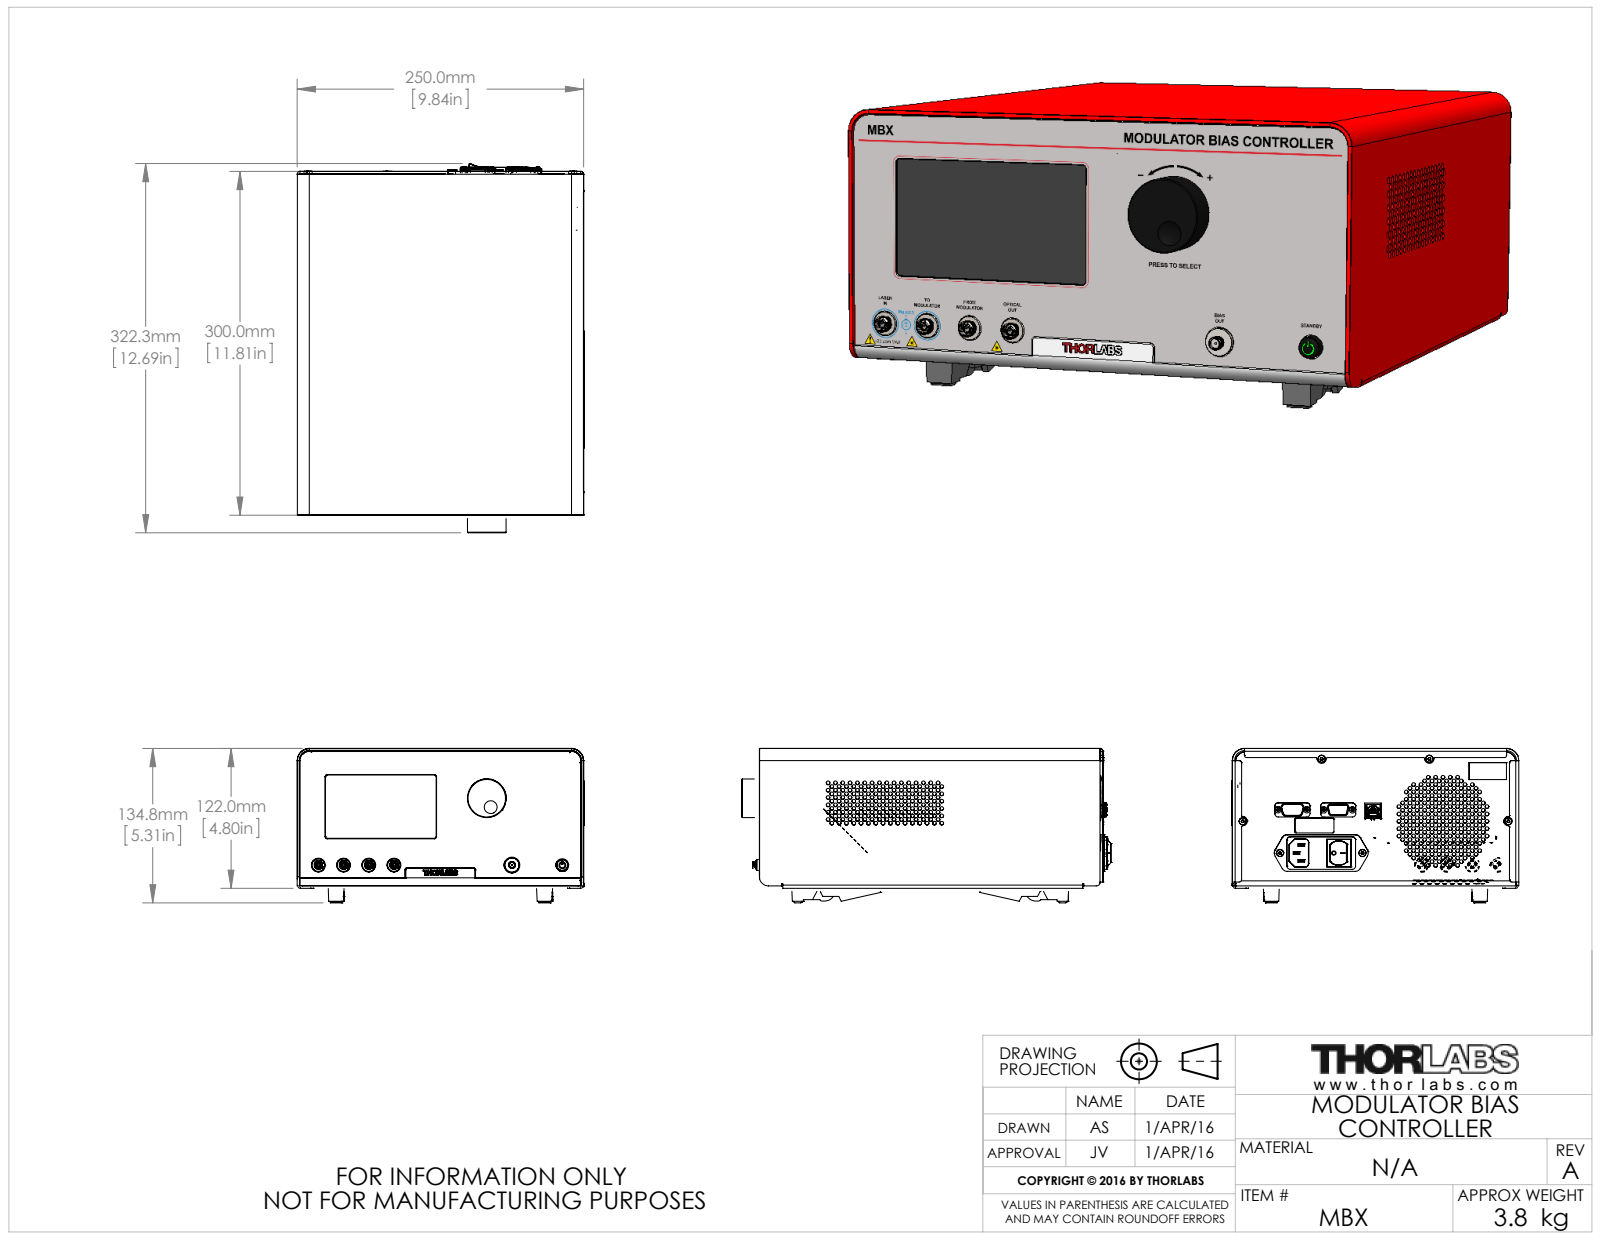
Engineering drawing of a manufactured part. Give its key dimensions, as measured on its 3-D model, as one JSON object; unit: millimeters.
{"part_name": "FAB-00052; EHW-00005; FAB-00014; FAS-00035 (+8 more)", "step_written_by": "SolidWorks 2014 (AUTOMOTIVE_DESIGN)", "units": "millimeters", "bodies": {"solids": 213, "faces": 12462, "planar": 3784, "cylindrical": 6273, "other": 2405}, "overall_size": [322.34, 250, 134.82], "volume_mm3": 844102, "surface_area_mm2": 851652, "round_holes": [[2, 482], [3.2, 459], [2.46, 37], [3.4, 28], [4.37, 25], [0.92, 15], [1.66, 15], [3.6, 8], [4.37, 8], [8.33, 6], [2.6, 5], [2.5, 4]], "round_bosses_or_shafts": [[3, 39], [4.35, 33], [3.48, 33], [6, 29], [2.35, 28], [3.91, 11], [1.02, 9], [4, 6]], "partial_cylinders_radius": [[2, 71], [0.5, 46], [1, 38], [0.25, 26], [0.15, 24], [3, 24], [0.2, 19], [0.3, 19]], "face_to_face_distances": [2, 118, 120, 116, 248, 293.65, 2.75, 245.25, 4.75, 243.25], "hole_center_spacings": [14.31, 6.4, 4.24, 9.05, 8.48, 12.72, 12.8, 16.96]}
